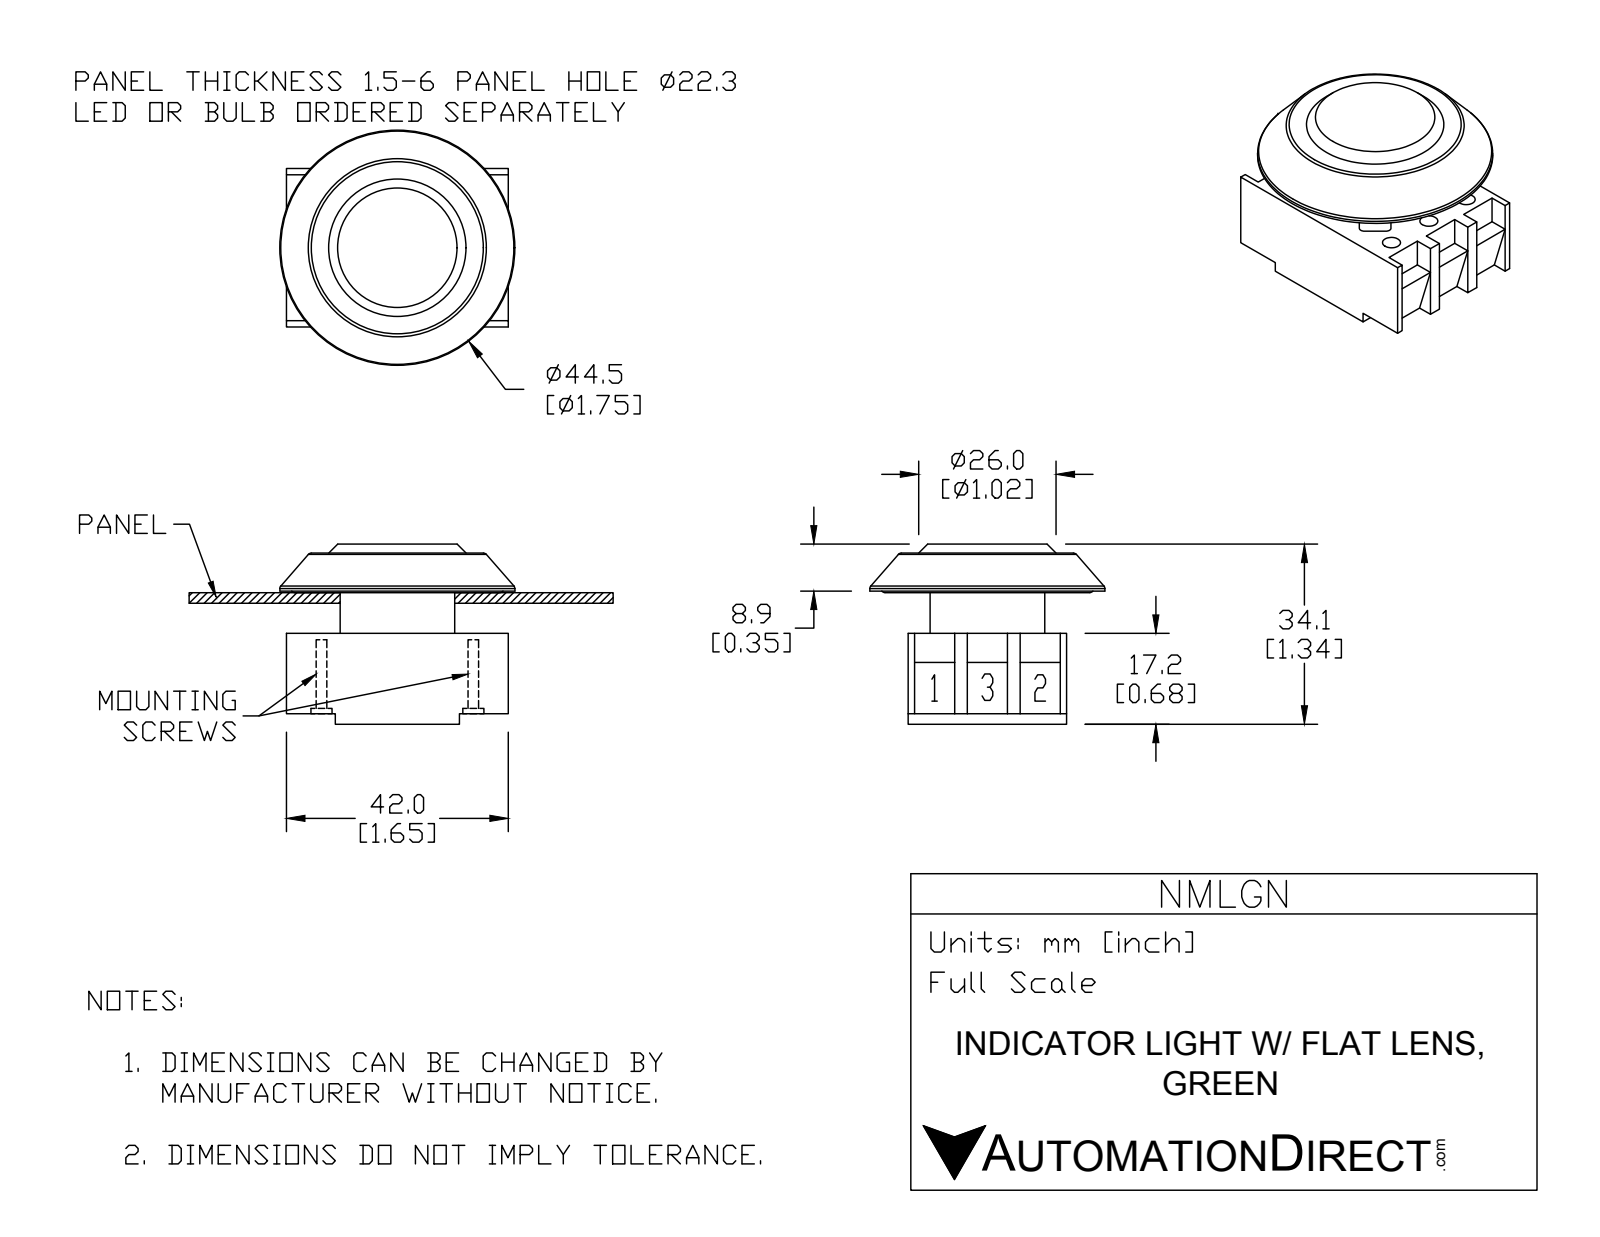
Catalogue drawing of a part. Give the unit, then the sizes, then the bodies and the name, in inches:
Units: inches
Overall size (bounding box): 1.752 × 1.752 × 1.343
Round holes (diameter × count): ⌀0.134 ×6, ⌀0.197 ×6, ⌀0.492 ×1
Round bosses / shafts (diameter × count): ⌀0.181 ×2, ⌀0.157 ×2, ⌀1.752 ×1, ⌀0.854 ×1
Partial cylindrical surfaces — rounded edges, fillets, slot ends (radius × count): R0.039 ×8, R0.343 ×5, R0.433 ×1
Main face-to-face distances: 1.181, 0.598, 0.315, 0.303, 0.362, 0.665, 0.35, 0.902, 0.394, 0.295
Hole centre spacings: 0.394, 0.69, 1.199, 1.132, 0.566, 0.787, 1.379
Volume: 1.461 in³ · Surface area: 23.46 in²
Bodies: 6 solids, 209 faces (125 planar, 63 cylindrical, 21 other)
Part name (STEP PRODUCT): NMLGN
STEP written by: SolidWorks 2015 (AUTOMOTIVE_DESIGN)
